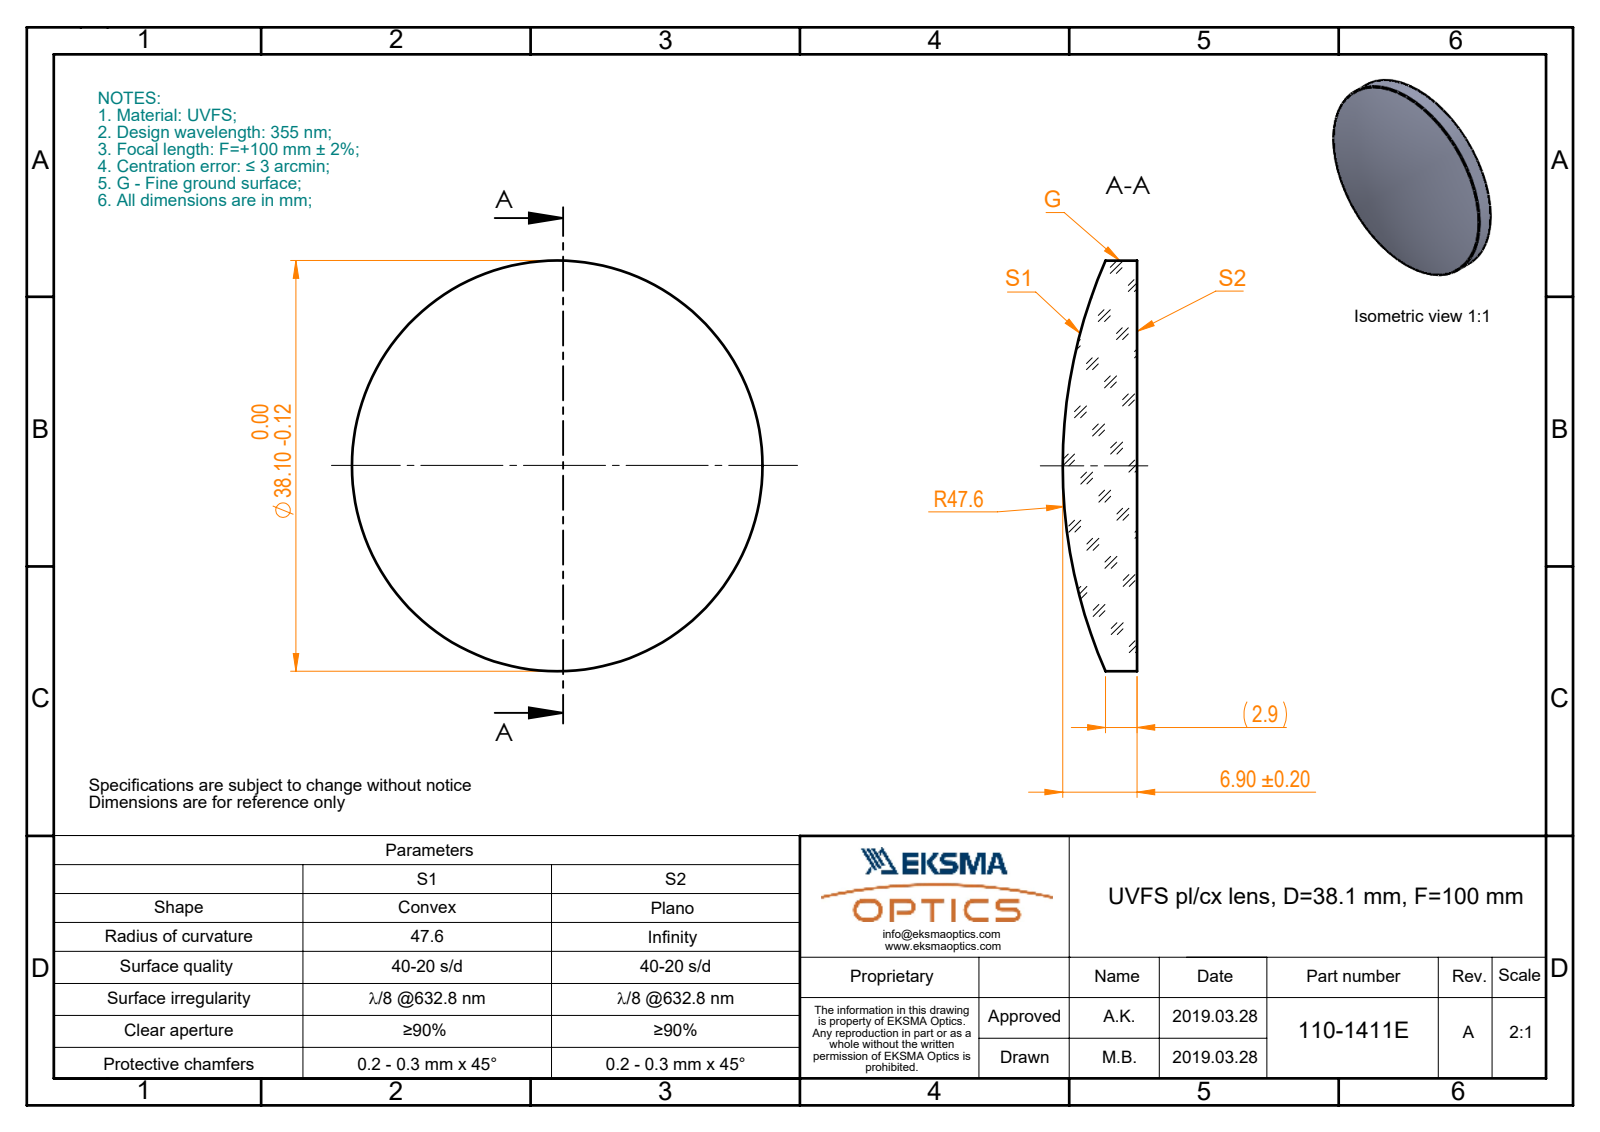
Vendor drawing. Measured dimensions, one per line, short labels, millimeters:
name: 110-1411E UVFS pl-cx 38.1 F100
written by: SolidWorks 2017 (CONFIG_CONTROL_DESIGN)
unit: mm
bodies: 1 solid, 5 faces (1 planar, 2 cylindrical, 2 other)
size: 38.1 × 38.1 × 6.9
volume: 5 632 mm³; area: 2 680 mm²
bosses: 1× ⌀38.1
